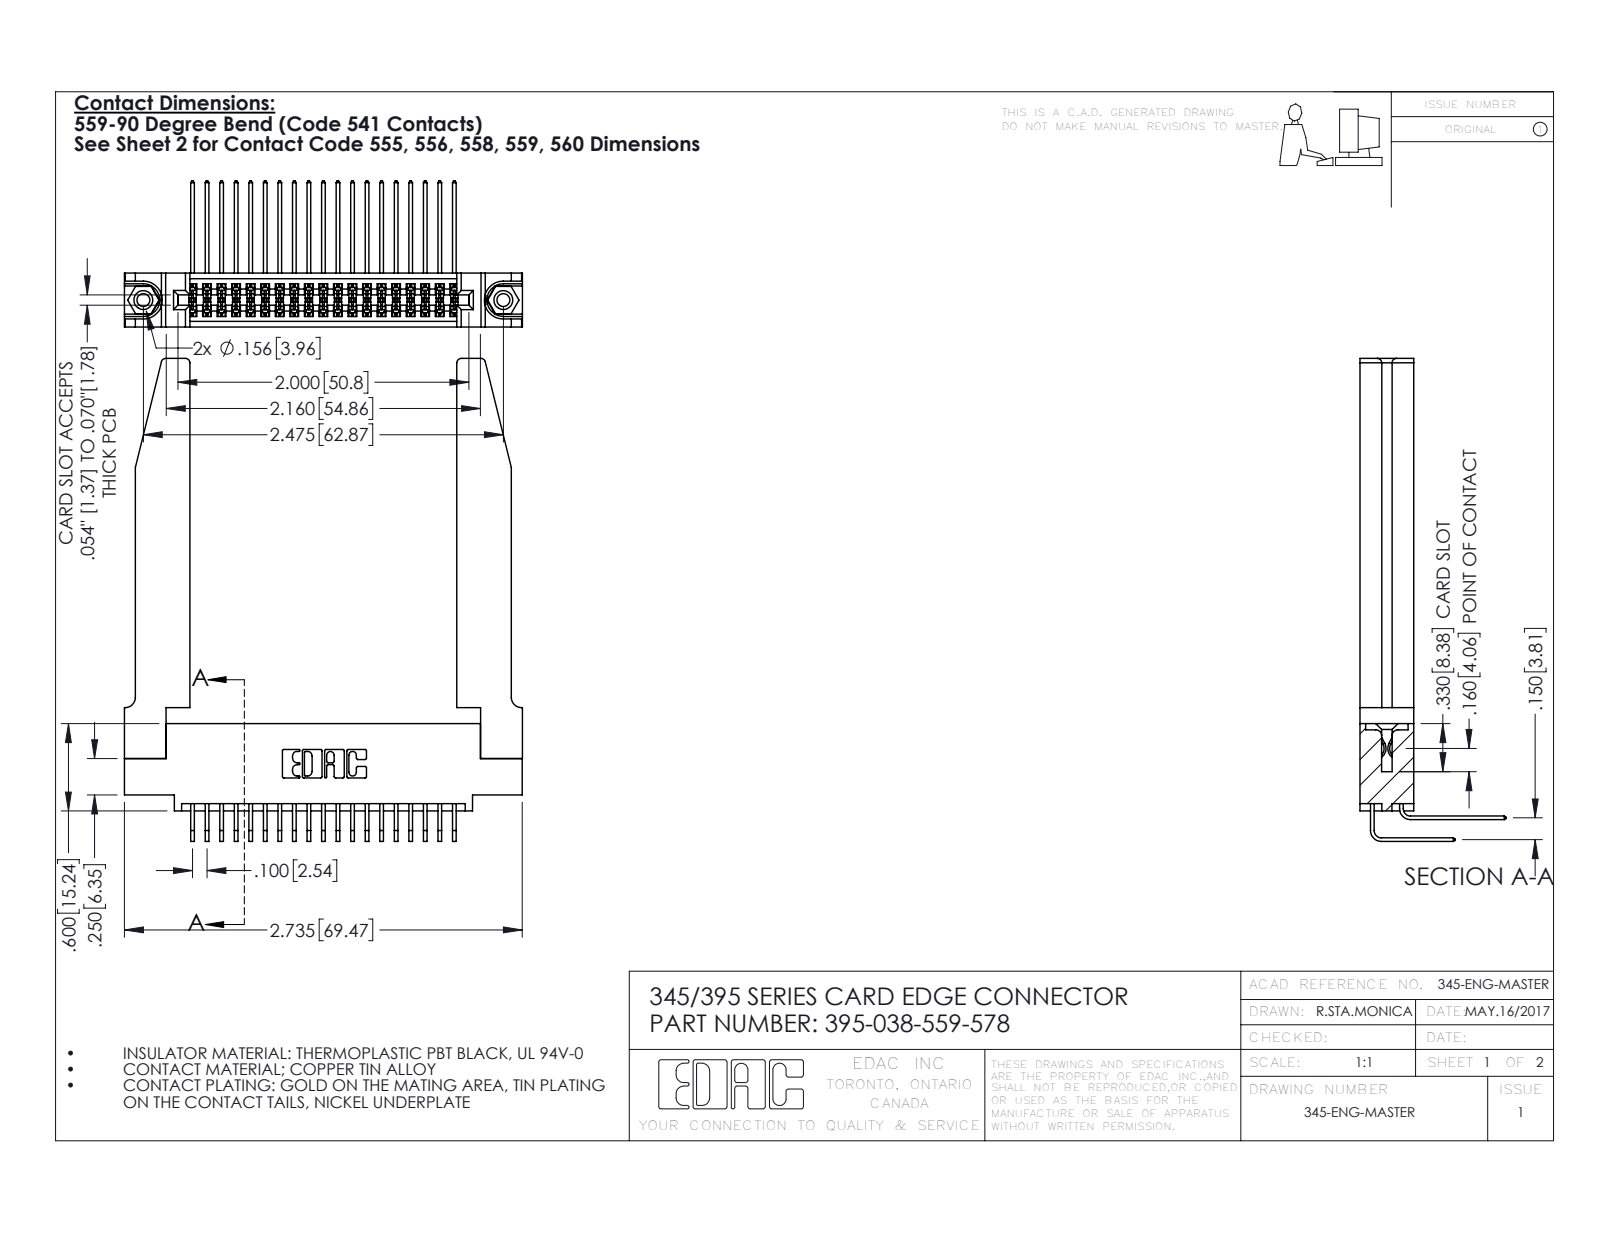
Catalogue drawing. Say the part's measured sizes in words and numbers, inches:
The part is named "345-292-001_558 559 Tail - 1; 345 Part_0.110 Offset - 0.156 Dia-TH; 345-250-001_345-250-001-102; 345-220-078_345-220-078 (+2 more)". Its 3-D file was written by "SolidWorks 2016 (CONFIG_CONTROL_DESIGN)". It is 43 solids with 2340 faces: 1556 planar, 732 cylindrical and 52 other. Overall it measures 3.319 by 2.736 by 1.005 inches. Its volume is 0.882 cubic inches and its surface area 26.96 square inches. Round holes: 2 of diameter 0.089, 2 of diameter 0.125, 2 of diameter 0.156, 1 of diameter 0.064. Round bosses or shafts: 2 of diameter 0.155. Partial cylindrical surfaces (rounded edges, fillets, slot ends): 58 of radius 0.006, 22 of radius 0.01, 8 of radius 0.03, 6 of radius 0.007, 6 of radius 0.031, 3 of radius 0.026, 2 of radius 0.014, 2 of radius 0.019. The main face-to-face distances are 0.37, 0.072, 0.298, 0.2, 0.098, 0.272, 0.025, 0.148, 0.15, 0.225. The hole center spacings are 0.27, 2.241, 2.475.
